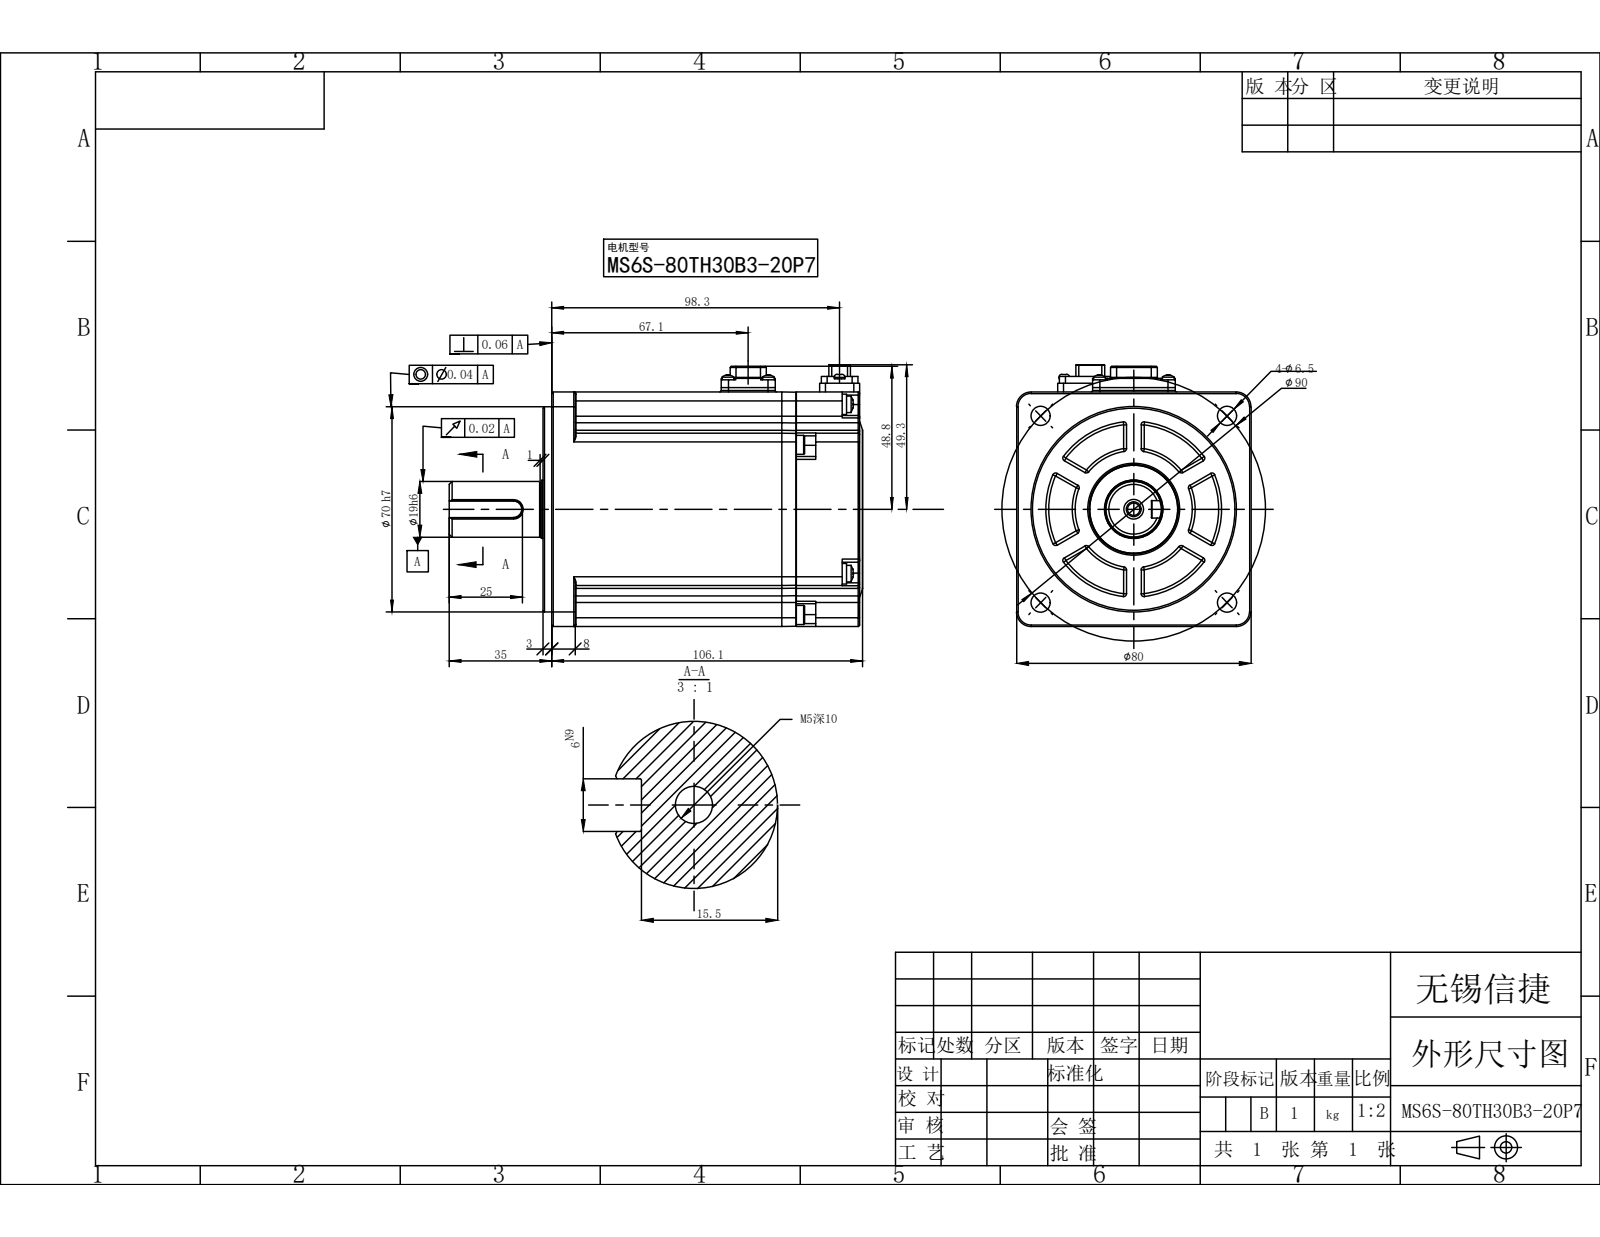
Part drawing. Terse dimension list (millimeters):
name: MS6S-80TH30B3-20P7
written by: SolidWorks 2022 (CONFIG_CONTROL_DESIGN)
unit: mm
bodies: 0 solids, 898 faces (388 planar, 301 cylindrical, 209 other)
size: 142.1 × 89.3 × 80
holes: 4× ⌀2.1, 4× ⌀6.5, 2× ⌀1.6, 1× ⌀4.2, 1× ⌀20
bosses: 8× ⌀7, 4× ⌀5.6, 4× ⌀4, 2× ⌀3.5, 1× ⌀70, 1× ⌀30, 1× ⌀19.8, 1× ⌀19
rounds: 50× R1, 39× R0.5, 17× R3, 16× R0.2, 16× R0.3, 12× R2, 8× R3.75, 4× R0.6
face distances: 80, 14, 66, 106.1, 1, 107.1, 3, 21.6, 52, 110.1
hole spacings: 45, 63.64, 8, 16.6, 18.43, 90, 23.5, 28.67
